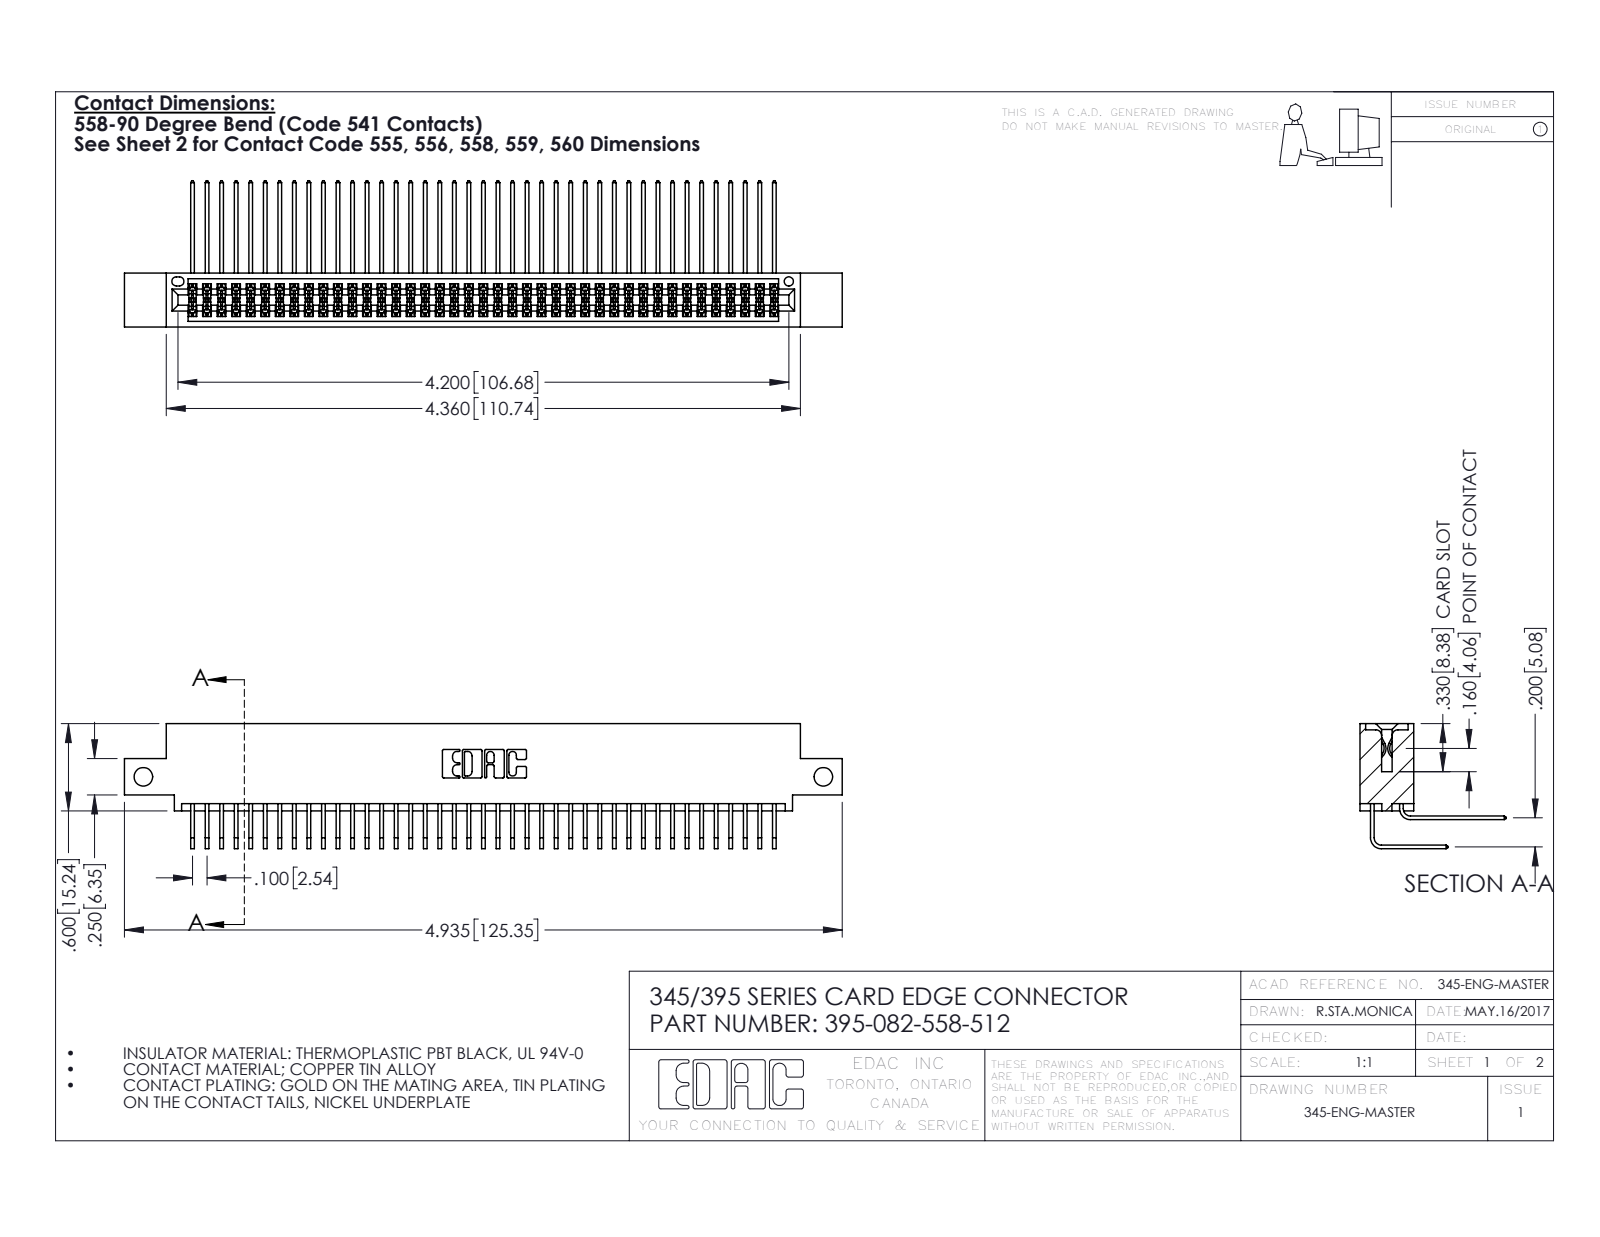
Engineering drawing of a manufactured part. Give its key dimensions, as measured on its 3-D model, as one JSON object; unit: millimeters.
{"part_name": "345-292-001_558 559 Tail - 1; 395-082-558-512; 345 Part_0.110 Offset - Side Mount; 345-292-001_558 Tail - 2", "step_written_by": "SolidWorks 2016 (CONFIG_CONTROL_DESIGN)", "units": "millimeters", "bodies": {"solids": 83, "faces": 4394, "planar": 2954, "cylindrical": 1440, "other": 0}, "overall_size": [125.3, 25.5, 21.8], "volume_mm3": 12500, "surface_area_mm2": 20610, "round_holes": [[3.3, 2], [1.6, 1]], "partial_cylinders_radius": [[0.2, 124], [0.3, 22], [0.2, 6], [0.8, 6], [0.7, 3], [0.4, 2], [0.5, 2], [0.6, 2]], "face_to_face_distances": [1.8, 7.6, 5.1, 9.4, 2.5, 6.9, 0.6, 5.7, 0.6, 4.4], "hole_center_spacings": [118.7]}
